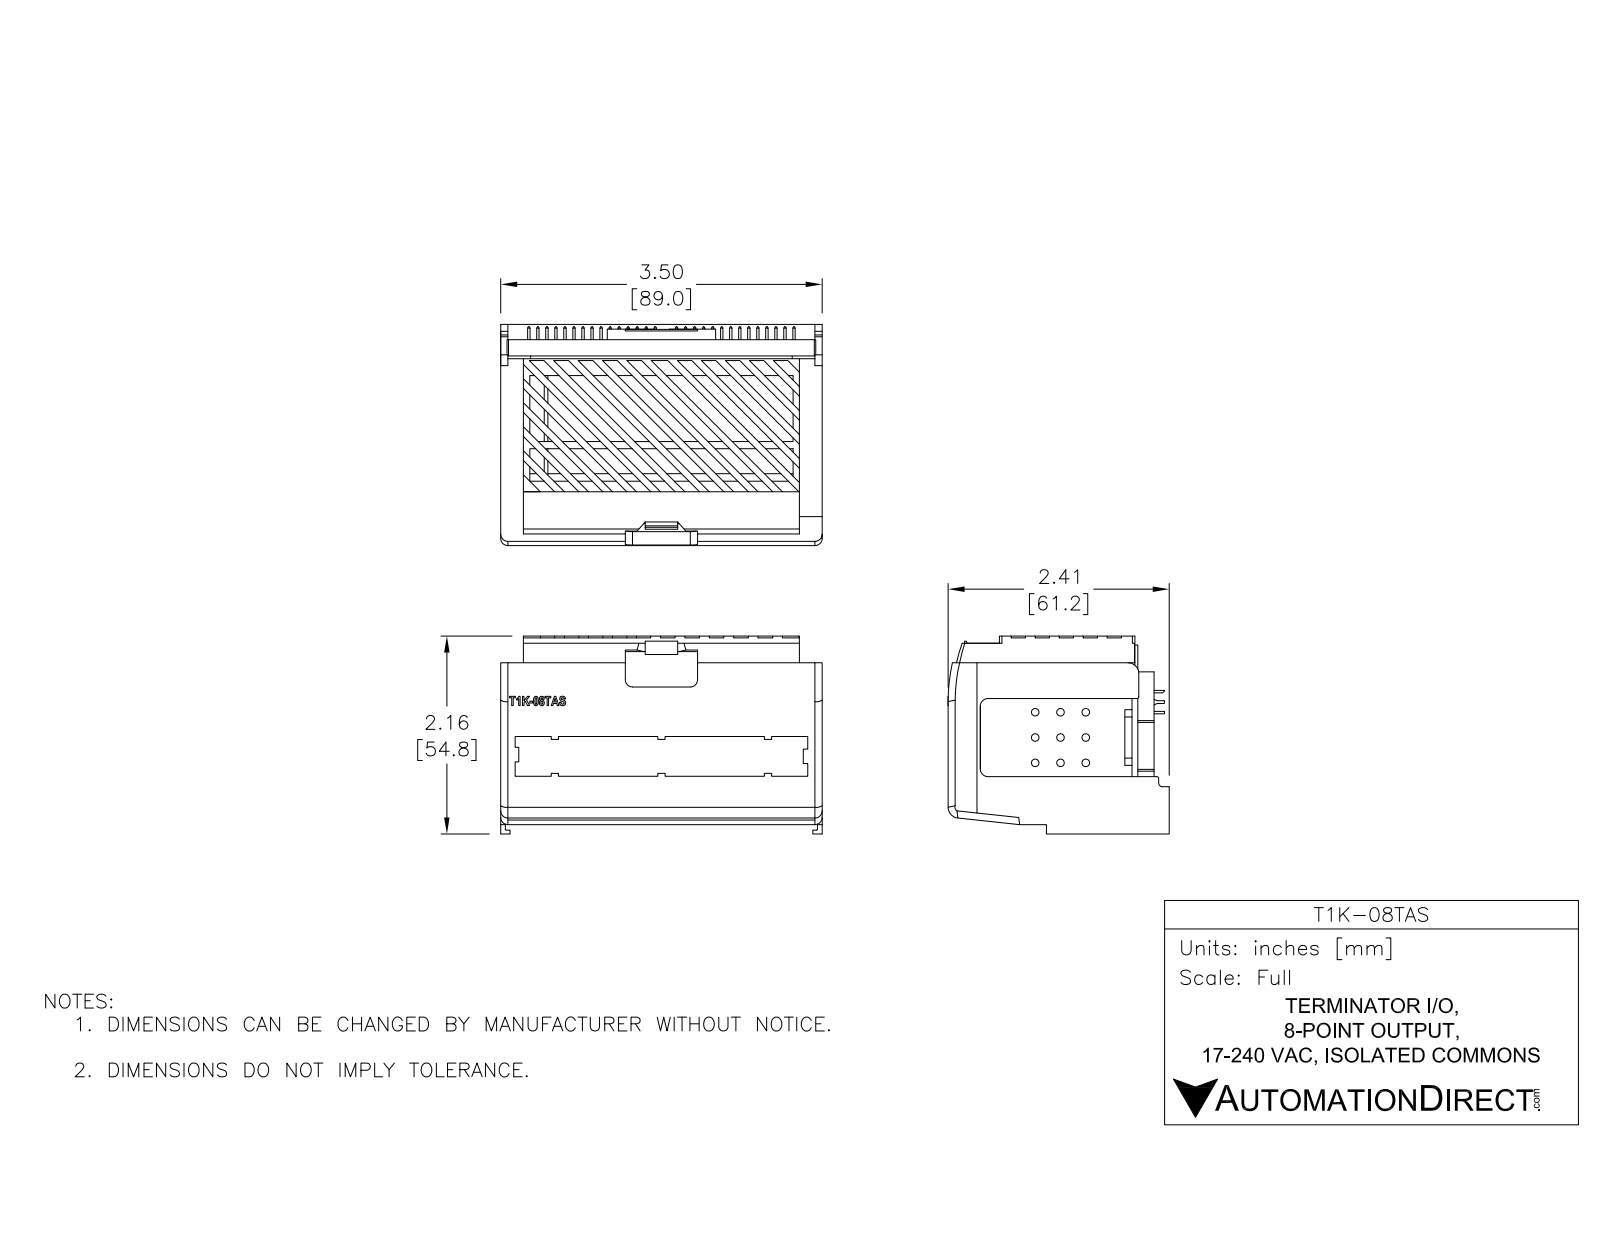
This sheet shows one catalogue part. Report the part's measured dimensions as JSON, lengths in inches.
{"part_name": "T1K-16TAS", "step_written_by": "SolidWorks 2013 (AUTOMOTIVE_DESIGN)", "units": "inches", "bodies": {"solids": 1, "faces": 647, "planar": 442, "cylindrical": 181, "other": 24}, "overall_size": [3.492, 2.563, 2.416], "volume_in3": 2.774, "surface_area_in2": 84.51, "round_holes": [[0.118, 16]], "round_bosses_or_shafts": [[0.028, 56]], "partial_cylinders_radius": [[0.138, 18], [0.039, 5], [0.01, 3], [0.022, 3], [0.059, 2], [0.315, 1], [0.394, 1], [0.709, 1]], "face_to_face_distances": [0.079, 3.413, 2.179, 0.02, 2.354, 3.492, 0.059, 2.176, 2.1, 3.335], "hole_center_spacings": [0.203, 0.406, 0.608, 0.811, 1.014, 1.217, 1.419, 1.622]}
